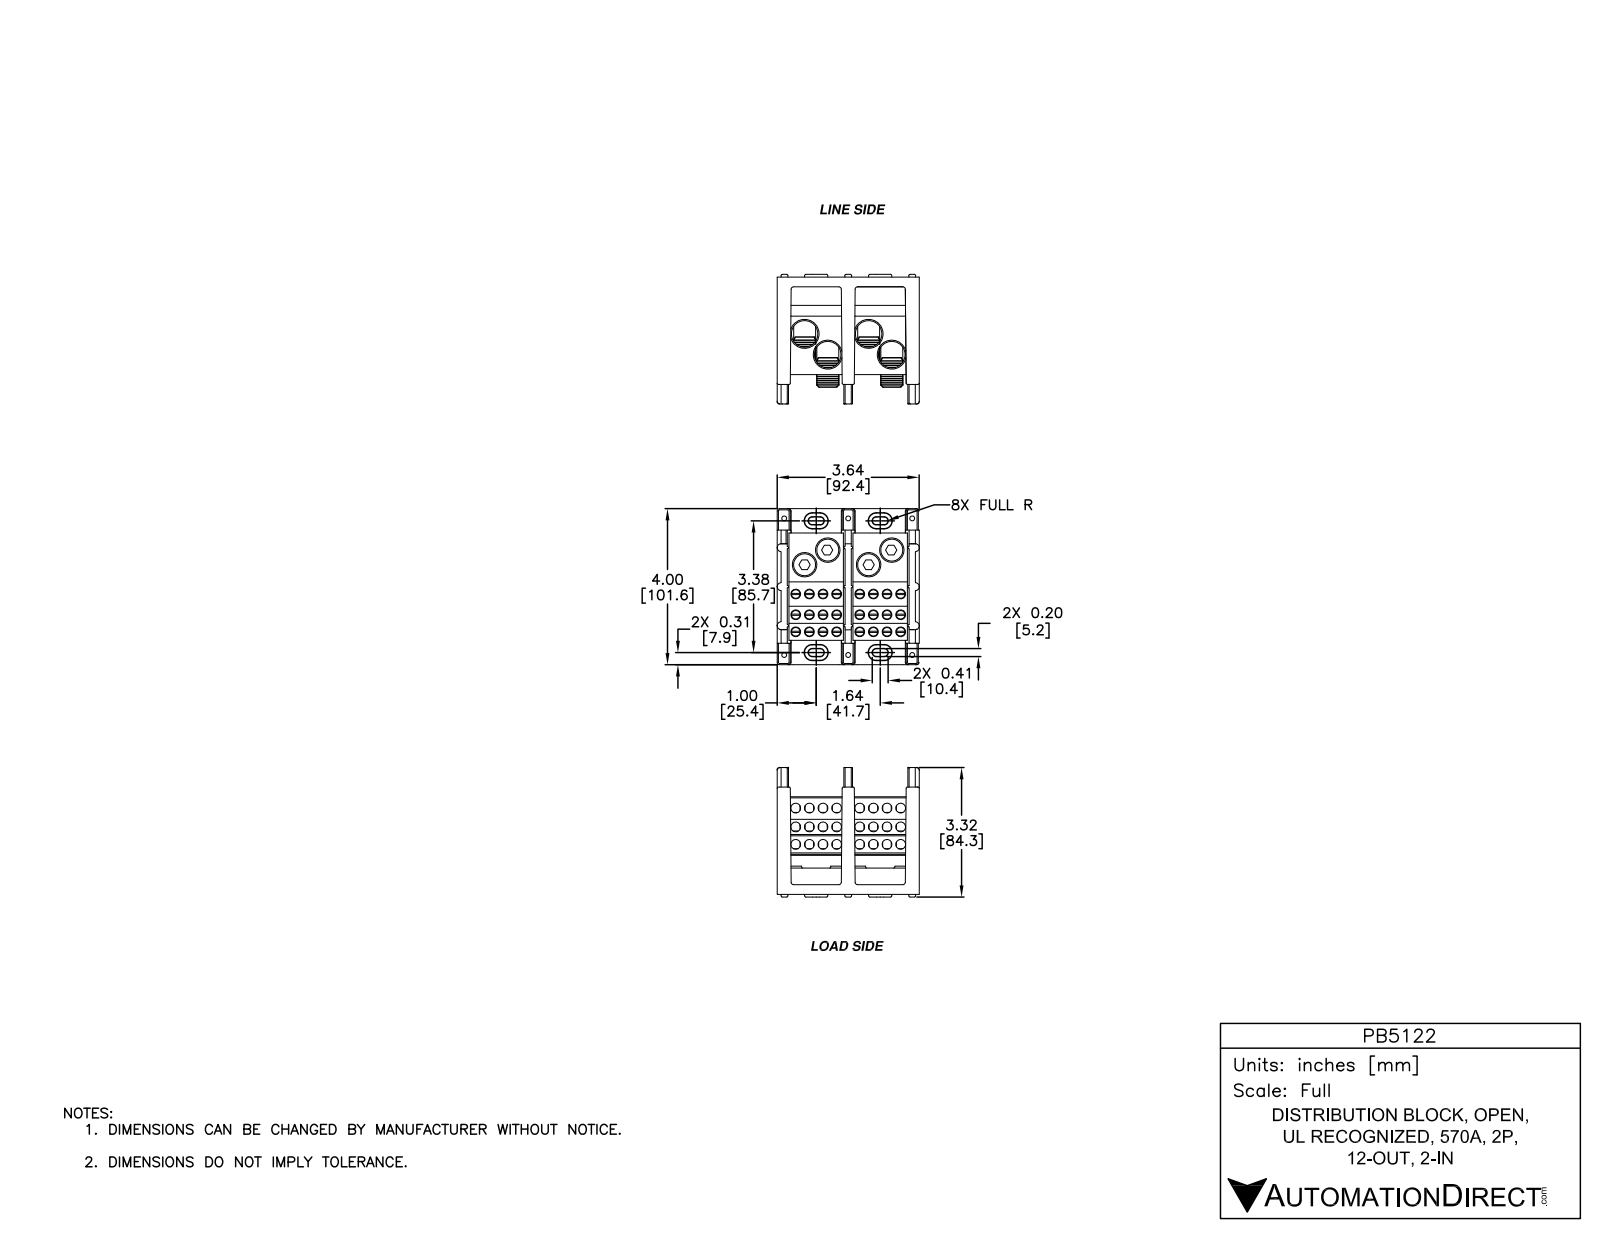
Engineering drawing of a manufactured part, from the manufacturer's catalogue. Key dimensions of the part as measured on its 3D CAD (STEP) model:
Part name (STEP PRODUCT): PB5122
STEP written by: SolidWorks 2014 (AUTOMOTIVE_DESIGN)
Units: inches
Bodies: 6 solids, 1273 faces (518 planar, 535 cylindrical, 220 other)
Overall size (bounding box): 4 × 3.641 × 3.35
Volume: 18.48 in³ · Surface area: 207.6 in²
Round holes (diameter × count): ⌀0.219 ×40, ⌀0.25 ×24, ⌀0.125 ×6, ⌀0.68 ×4, ⌀0.563 ×3, ⌀0.5 ×2, ⌀0.75 ×1
Round bosses / shafts (diameter × count): ⌀0.174 ×6, ⌀0.062 ×4, ⌀0.563 ×3, ⌀0.375 ×2
Partial cylindrical surfaces — rounded edges, fillets, slot ends (radius × count): R0.031 ×64, R0.1 ×38, R0.063 ×25, R0.062 ×20, R0.203 ×18, R0.094 ×8
Main face-to-face distances: 1.641, 0.159, 1.481, 0.1, 1.8, 3.281, 1.9, 0.259, 1.741, 3.381
Hole centre spacings: 0.349, 0.699, 1.641, 0.636, 0.35, 0.993, 1.048, 2.34
